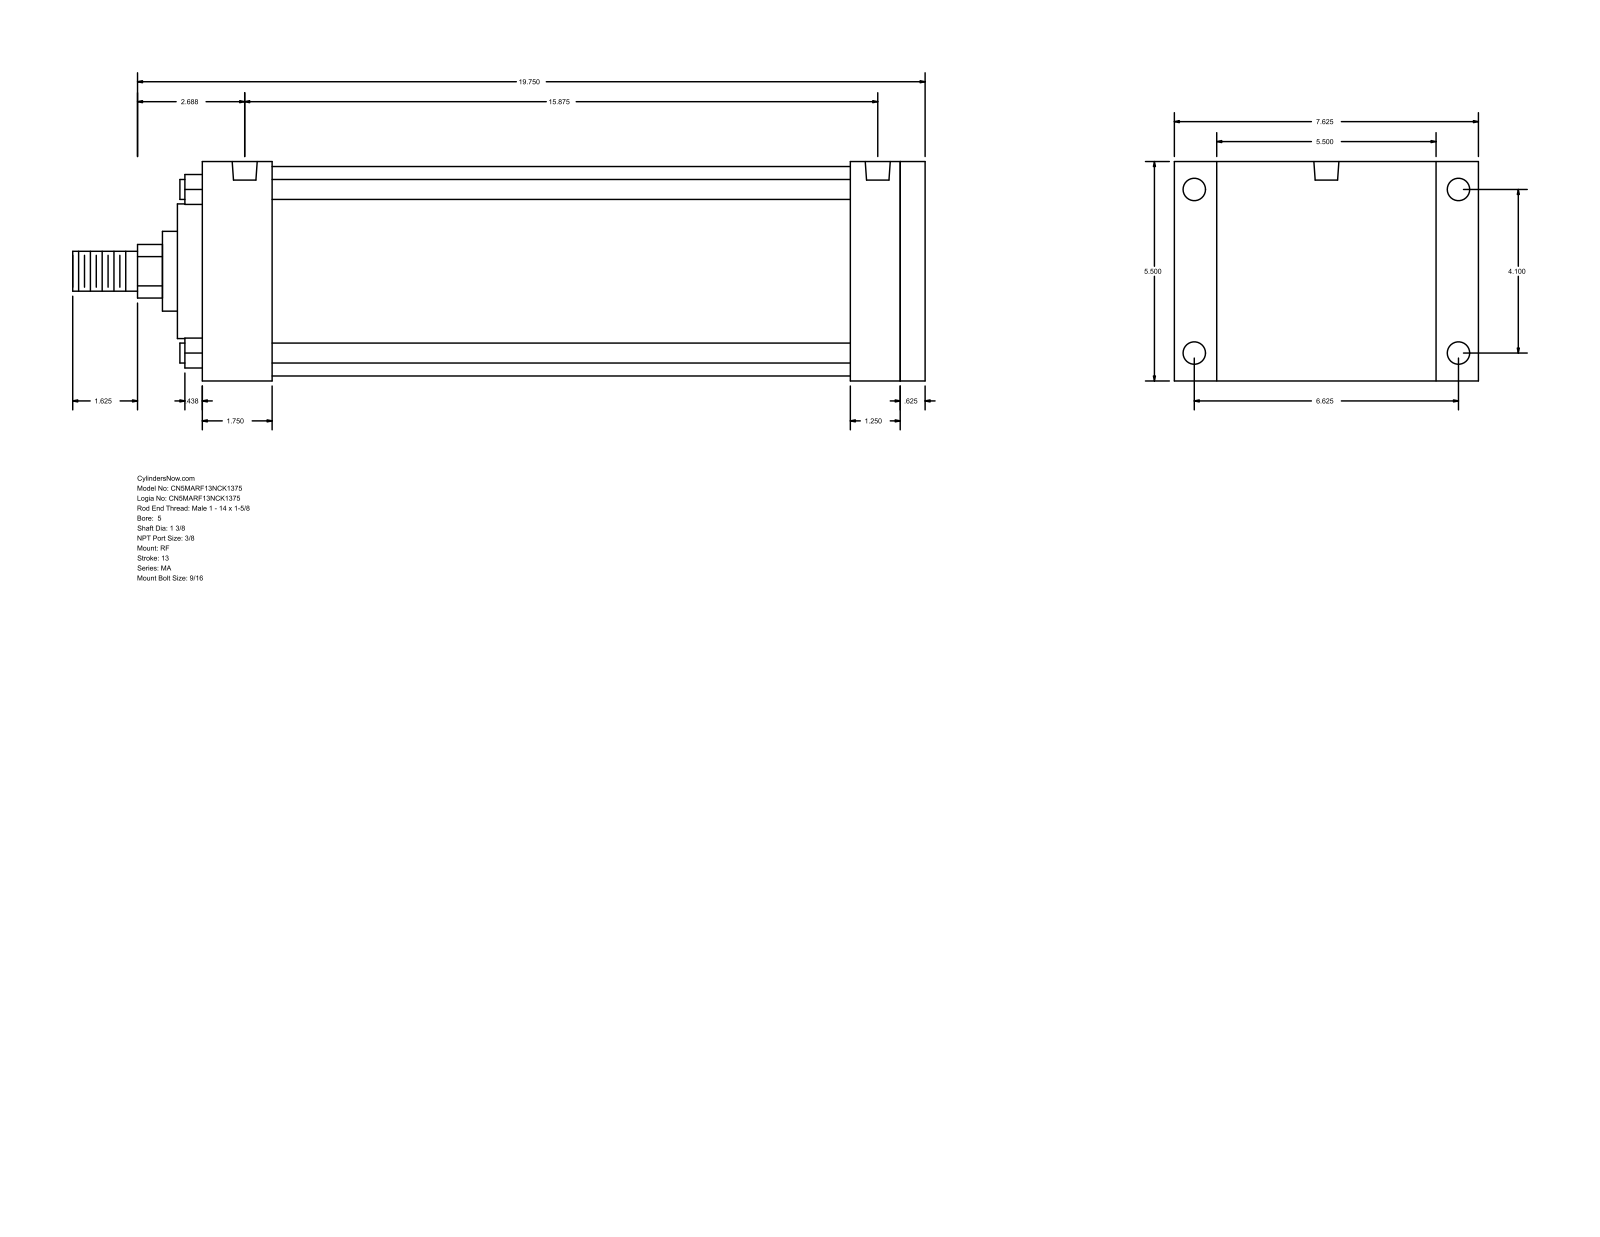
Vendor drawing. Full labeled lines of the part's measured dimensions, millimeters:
Part name (STEP PRODUCT): MA_RF__0500_1.375
STEP written by: GSSL Pune (CONFIG_CONTROL_DESIGN)
Units: millimetres
Bodies: 0 solids, 94 faces (65 planar, 29 cylindrical, 0 other)
Overall size (bounding box): 542.92 × 193.68 × 139.7
Round holes (diameter × count): ⌀11.11 ×4, ⌀14.29 ×4, ⌀15.93 ×2
Round bosses / shafts (diameter × count): ⌀12.7 ×4, ⌀133.35 ×1, ⌀85.72 ×1, ⌀50.8 ×1, ⌀34.92 ×1, ⌀25.4 ×1
Partial cylindrical surfaces — rounded edges, fillets, slot ends (radius × count): R17.06 ×1
Main face-to-face distances: 139.7, 460.38, 15.88, 444.5, 44.45, 400.05, 415.93, 412.75, 368.3, 31.75
Hole centre spacings: 104.14, 168.28, 197.9, 393.7, 4.76, 4.77, 398.46, 398.47
